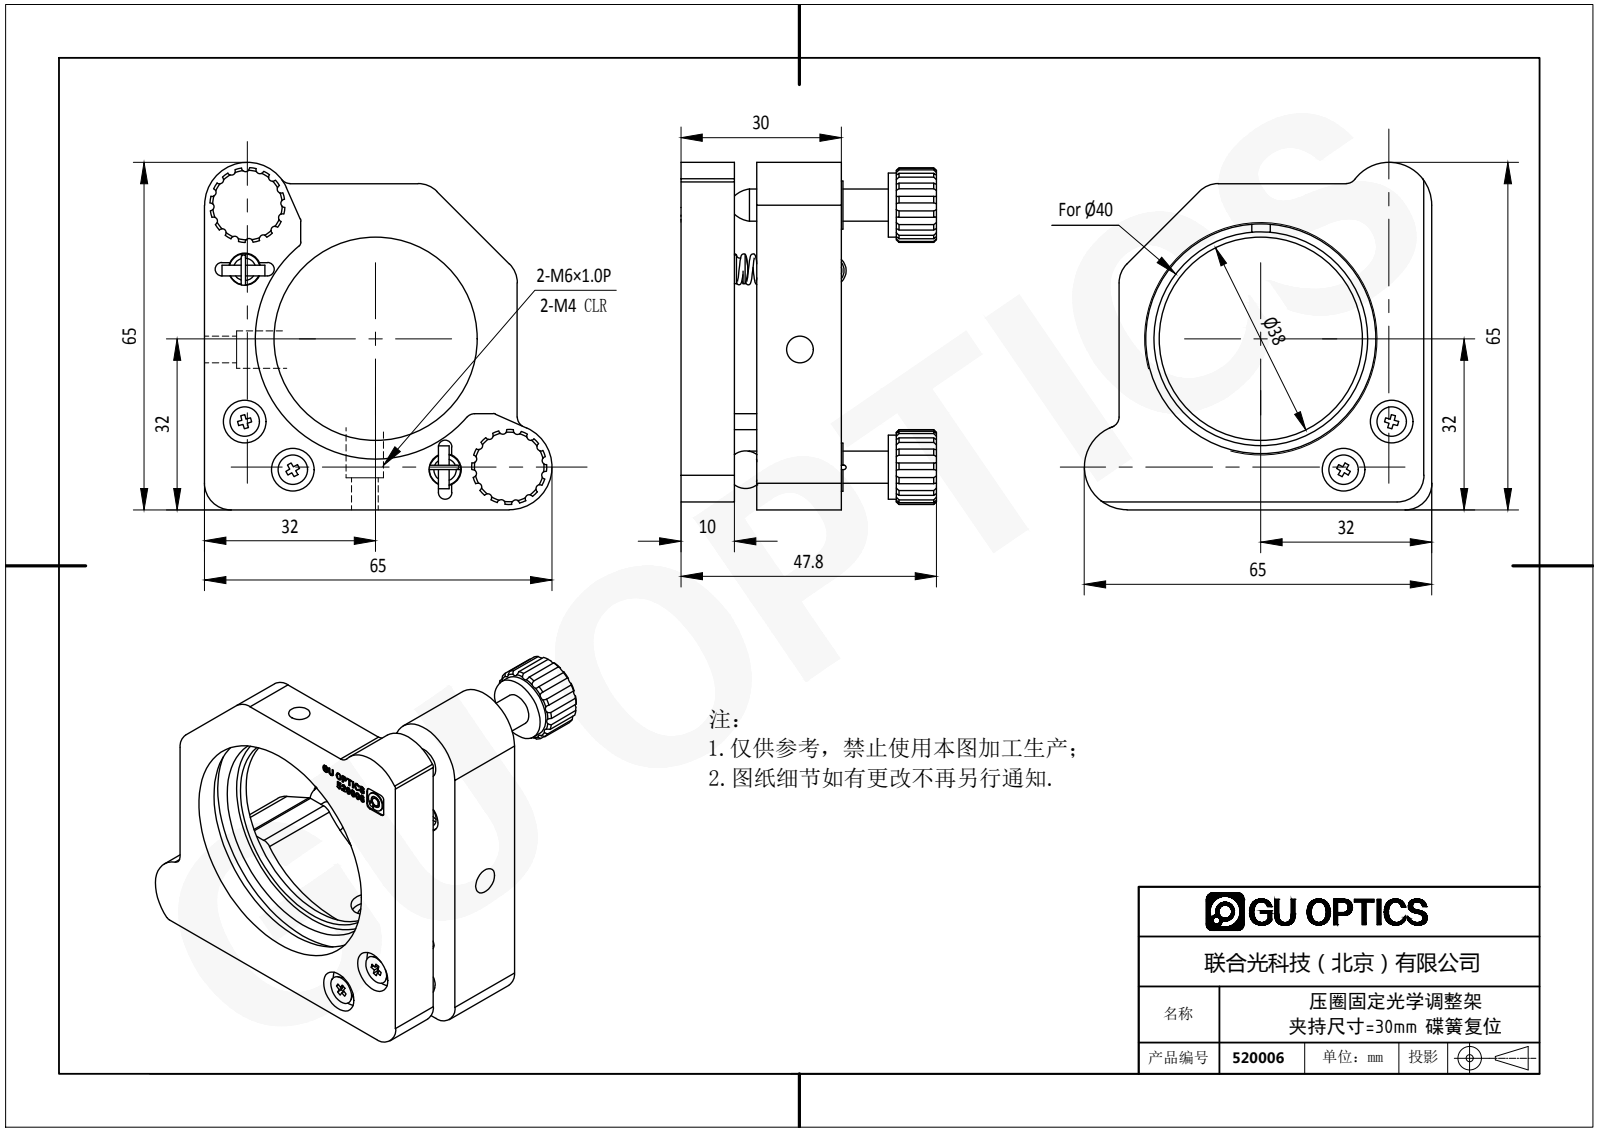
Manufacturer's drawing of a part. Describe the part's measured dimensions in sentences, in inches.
The part is named "520006". Its 3-D file was written by "SolidWorks 2016 (AUTOMOTIVE_DESIGN)". It is 0 solids with 593 faces: 193 planar, 193 cylindrical and 207 other. Overall it measures 2.559 by 2.559 by 1.882 inches. Round holes: 4 of diameter 0.236, 4 of diameter 0.315, 3 of diameter 0.157, 2 of diameter 0.197, 2 of diameter 0.295, 1 of diameter 1.496, 1 of diameter 1.575, 1 of diameter 1.693, 1 of diameter 1.772. Round bosses or shafts: 2 of diameter 0.472, 2 of diameter 0.354, 2 of diameter 0.213, 2 of diameter 0.118, 2 of diameter 0.079, 2 of diameter 0.031. Partial cylindrical surfaces (rounded edges, fillets, slot ends): 32 of radius 0.03, 5 of radius 0.039, 4 of radius 0.049, 4 of radius 0.197, 3 of radius 0.079, 2 of radius 0.276, 2 of radius 0.315. The main face-to-face distances are 0.394, 0.059, 0.165, 0.559, 0.622, 0.787, 1.181, 0.236, 0.157, 0.098. The hole center spacings are 0.473, 1.092, 1.122, 1.141, 1.365, 1.518, 1.594, 1.977.
